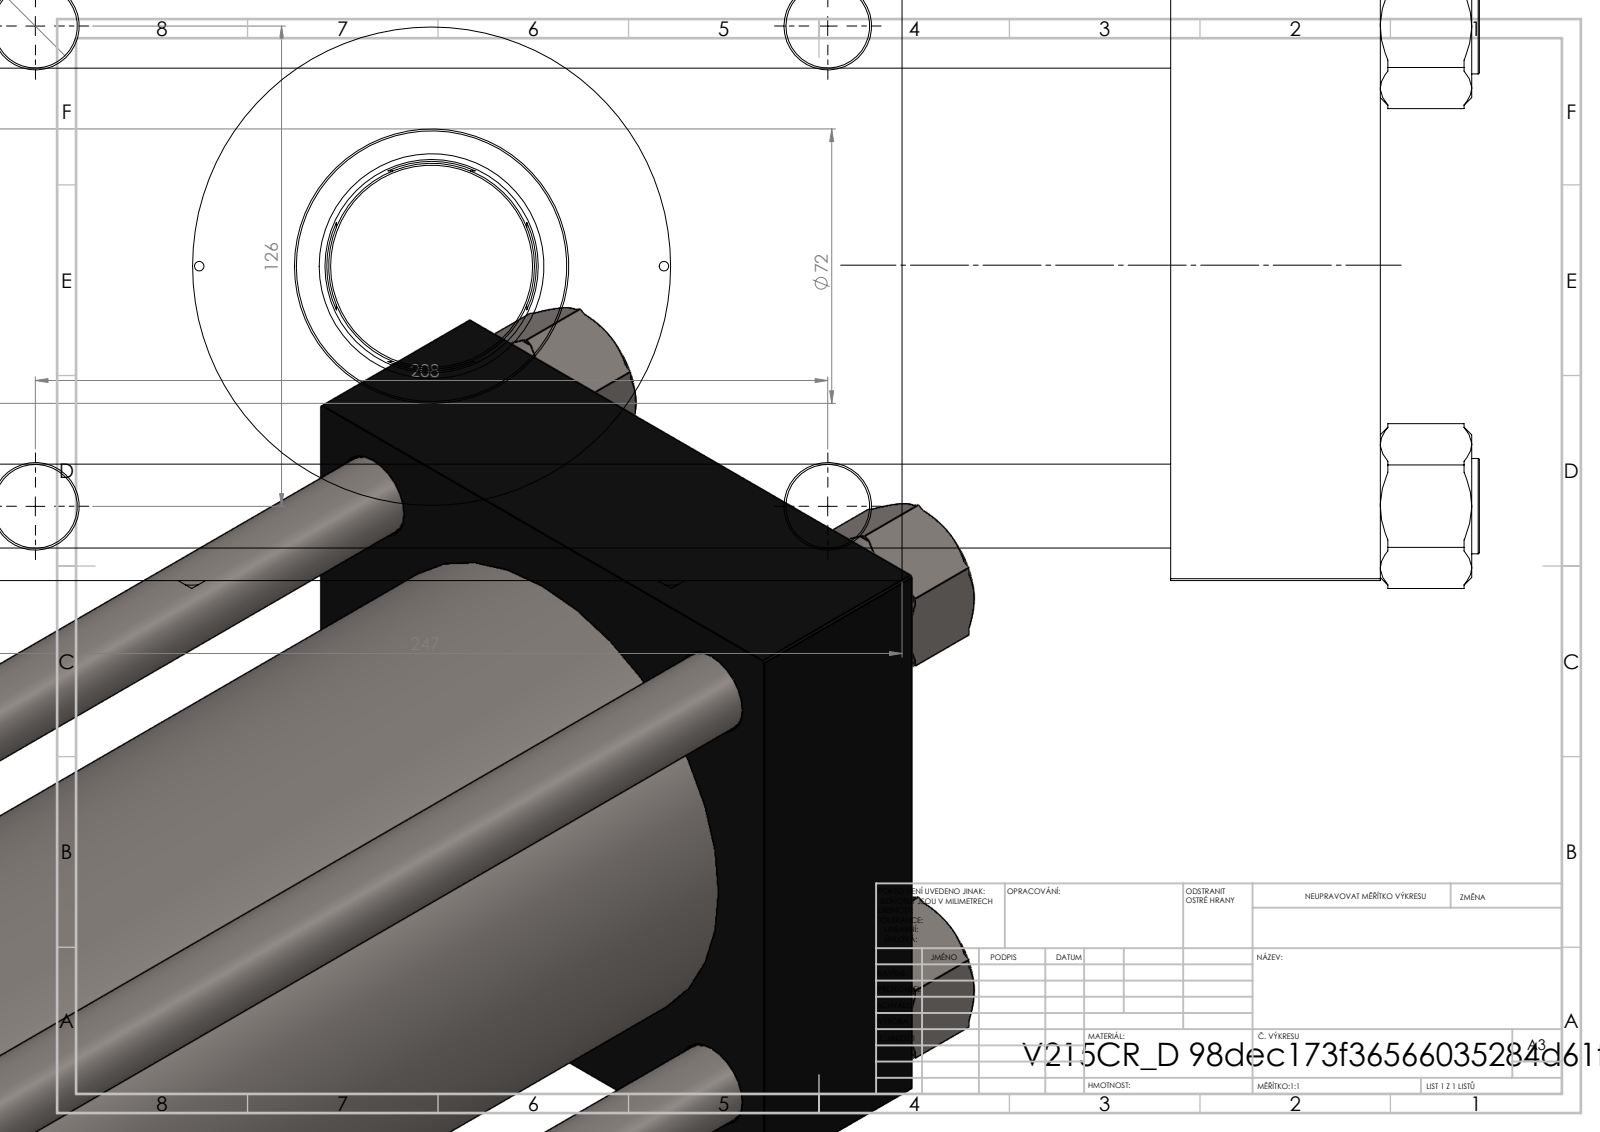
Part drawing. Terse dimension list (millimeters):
name: V215CR_D_TYCINKA; V215CR_VCP_D; V215_VC_A; NUT_M5_D (+2 more)
written by: SolidWorks 2019 (CONFIG_CONTROL_DESIGN)
unit: mm
bodies: 12 solids, 1168 faces (550 planar, 94 cylindrical, 524 other)
size: 560 × 247 × 169.14
volume: 6 210 000 mm³; area: 835 703 mm²
holes: 8× ⌀22, 2× ⌀2.5, 2× ⌀7, 2× ⌀32.24, 2× ⌀45, 1× ⌀40.5, 1× ⌀56, 1× ⌀59, 1× ⌀96, 1× ⌀125, 1× ⌀125.5
bosses: 4× ⌀25, 1× ⌀131, 1× ⌀72, 1× ⌀54, 1× ⌀40
face distances: 165, 314, 55, 369, 56, 425, 370, 41, 206, 403.74
hole spacings: 41.05, 62.98, 76.28, 89.02, 121.59, 125.9, 132.47, 139.02
